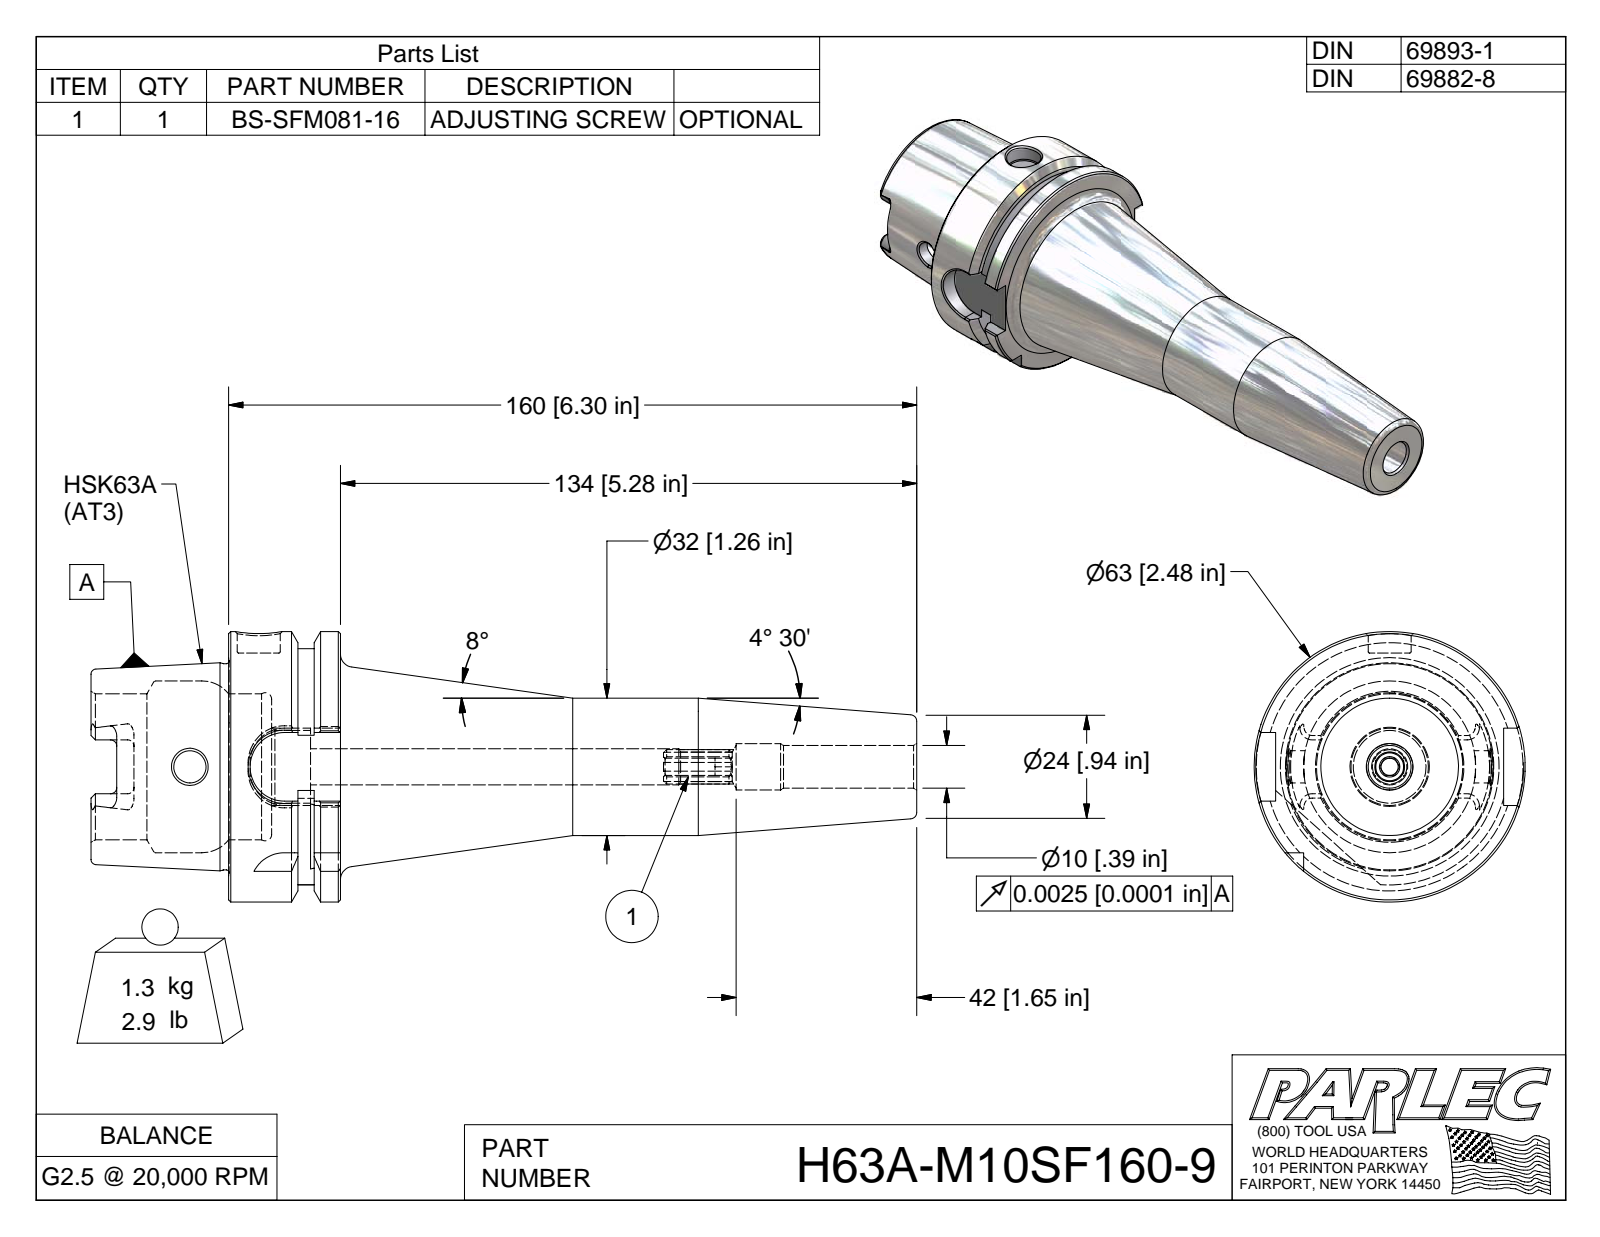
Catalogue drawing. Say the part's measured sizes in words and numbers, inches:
The part is named "H63A-M10SF160-9; H63A-M10SF160-9-1; BS-SFM081-16". Its 3-D file was written by "Autodesk Inventor 2009 (AUTOMOTIVE_DESIGN)". It is 2 solids with 160 faces: 59 planar, 35 cylindrical and 66 other. Overall it measures 7.559 by 2.48 by 2.48 inches. Its volume is 11.98 cubic inches and its surface area 61.07 square inches. Round holes: 1 of diameter 0.295, 1 of diameter 0.393, 1 of diameter 0.394, 1 of diameter 0.423, 1 of diameter 0.666, 1 of diameter 1.339, 1 of diameter 1.575. Round bosses or shafts: 1 of diameter 2.48, 1 of diameter 1.891, 1 of diameter 1.26. Partial cylindrical surfaces (rounded edges, fillets, slot ends): 6 of radius 0.059, 4 of radius 0.113, 4 of radius 0.315, 1 of radius 0.157, 1 of radius 1.083. The main face-to-face distances are 1.024, 0.241, 0.389, 0.394, 0.63, 1.26, 1.654, 2.283, 1.894, 0.635.
